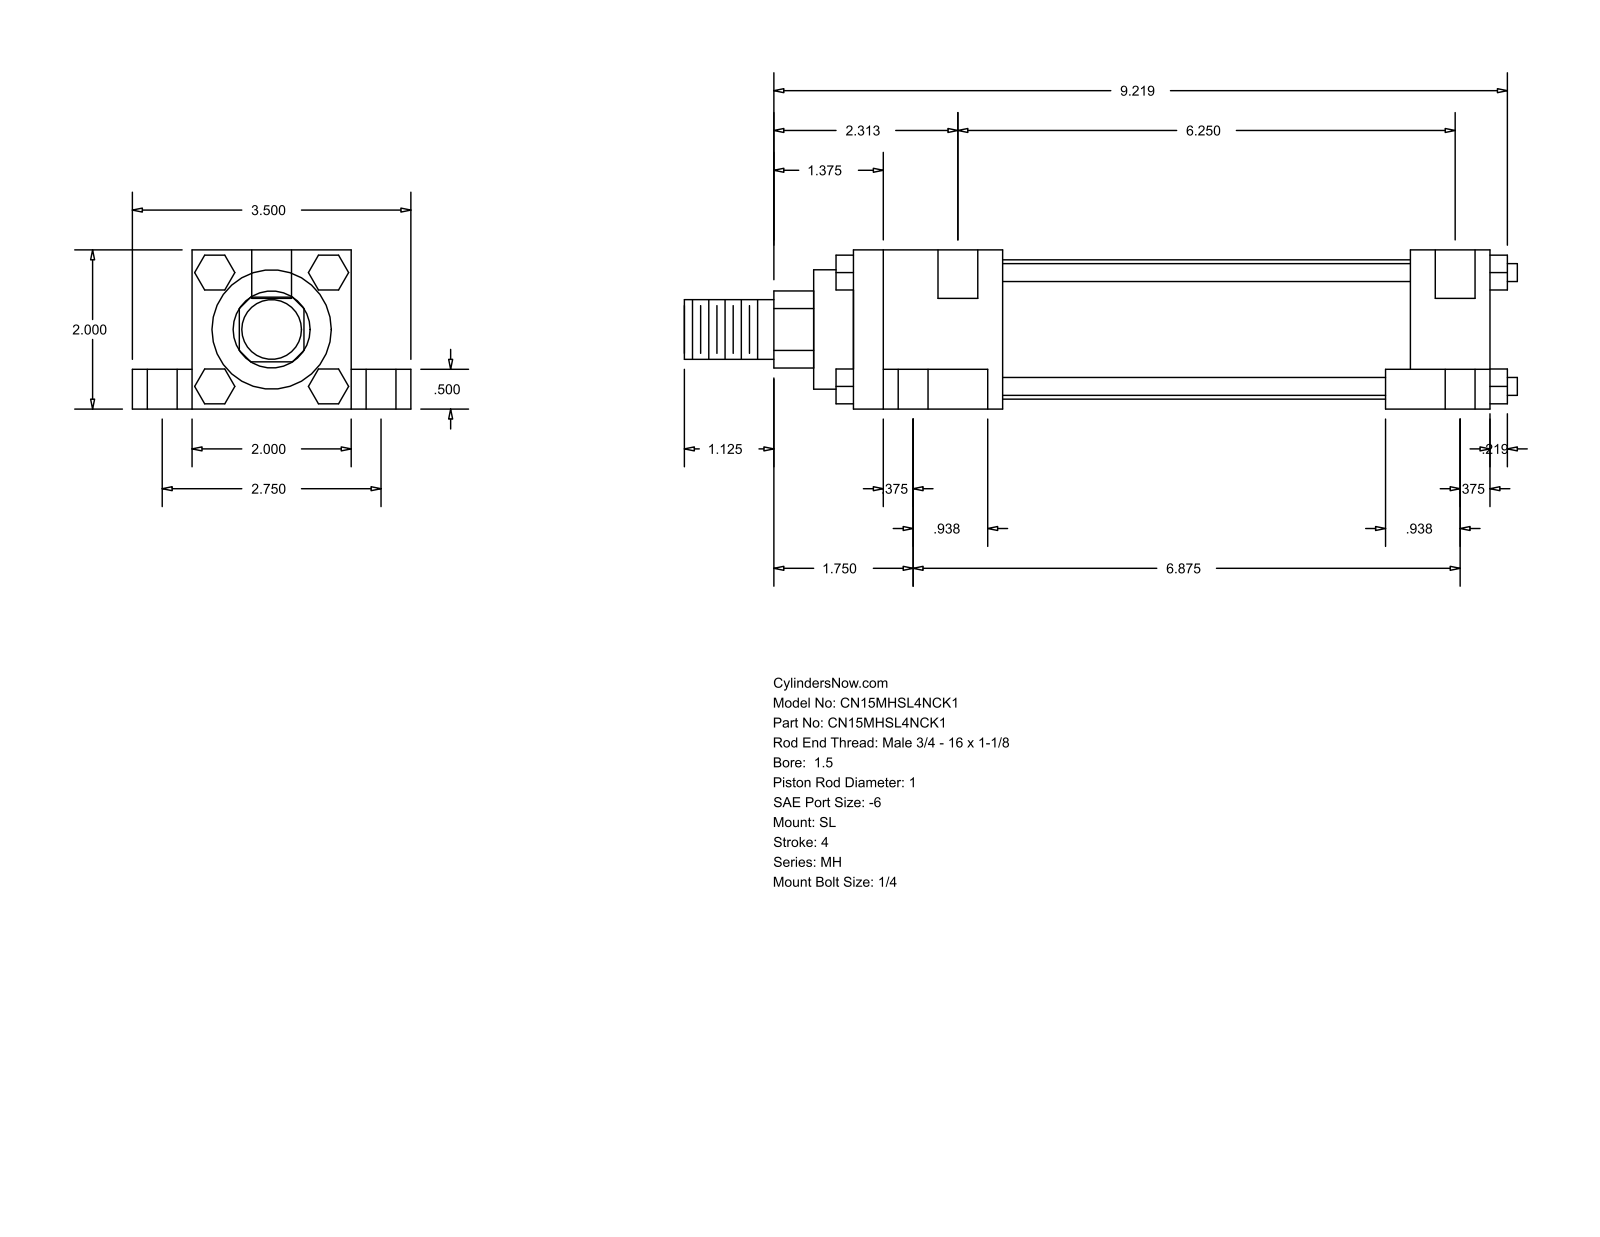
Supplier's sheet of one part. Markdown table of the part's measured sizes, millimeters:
| quantity | value |
| --- | --- |
| part name | MH_SL__0150_1 |
| STEP written by | GSSL Pune (CONFIG_CONTROL_DESIGN) |
| units | millimeters |
| bodies | 0 solids, 148 faces (112 planar, 36 cylindrical, 0 other) |
| overall size | 265.91 × 88.9 × 50.8 |
| round holes (diameter × count) | 5.56 × 4, 9.53 × 4, 15.88 × 4, 12.7 × 2 |
| round bosses / shafts (diameter × count) | 5.71 × 4, 44.45 × 1, 38.1 × 1, 25.4 × 1, 19.05 × 1 |
| partial cylindrical surfaces (radius × count) | 12.29 × 1 |
| main face-to-face distances | 50.8, 12.7, 38.1, 19.05, 69.85, 203.2, 25.4, 9.52, 33.34, 160.34 |
| hole center spacings | 34.96, 36.64, 37.73, 69.84, 161.93, 164.09, 167.2, 174.62 |
